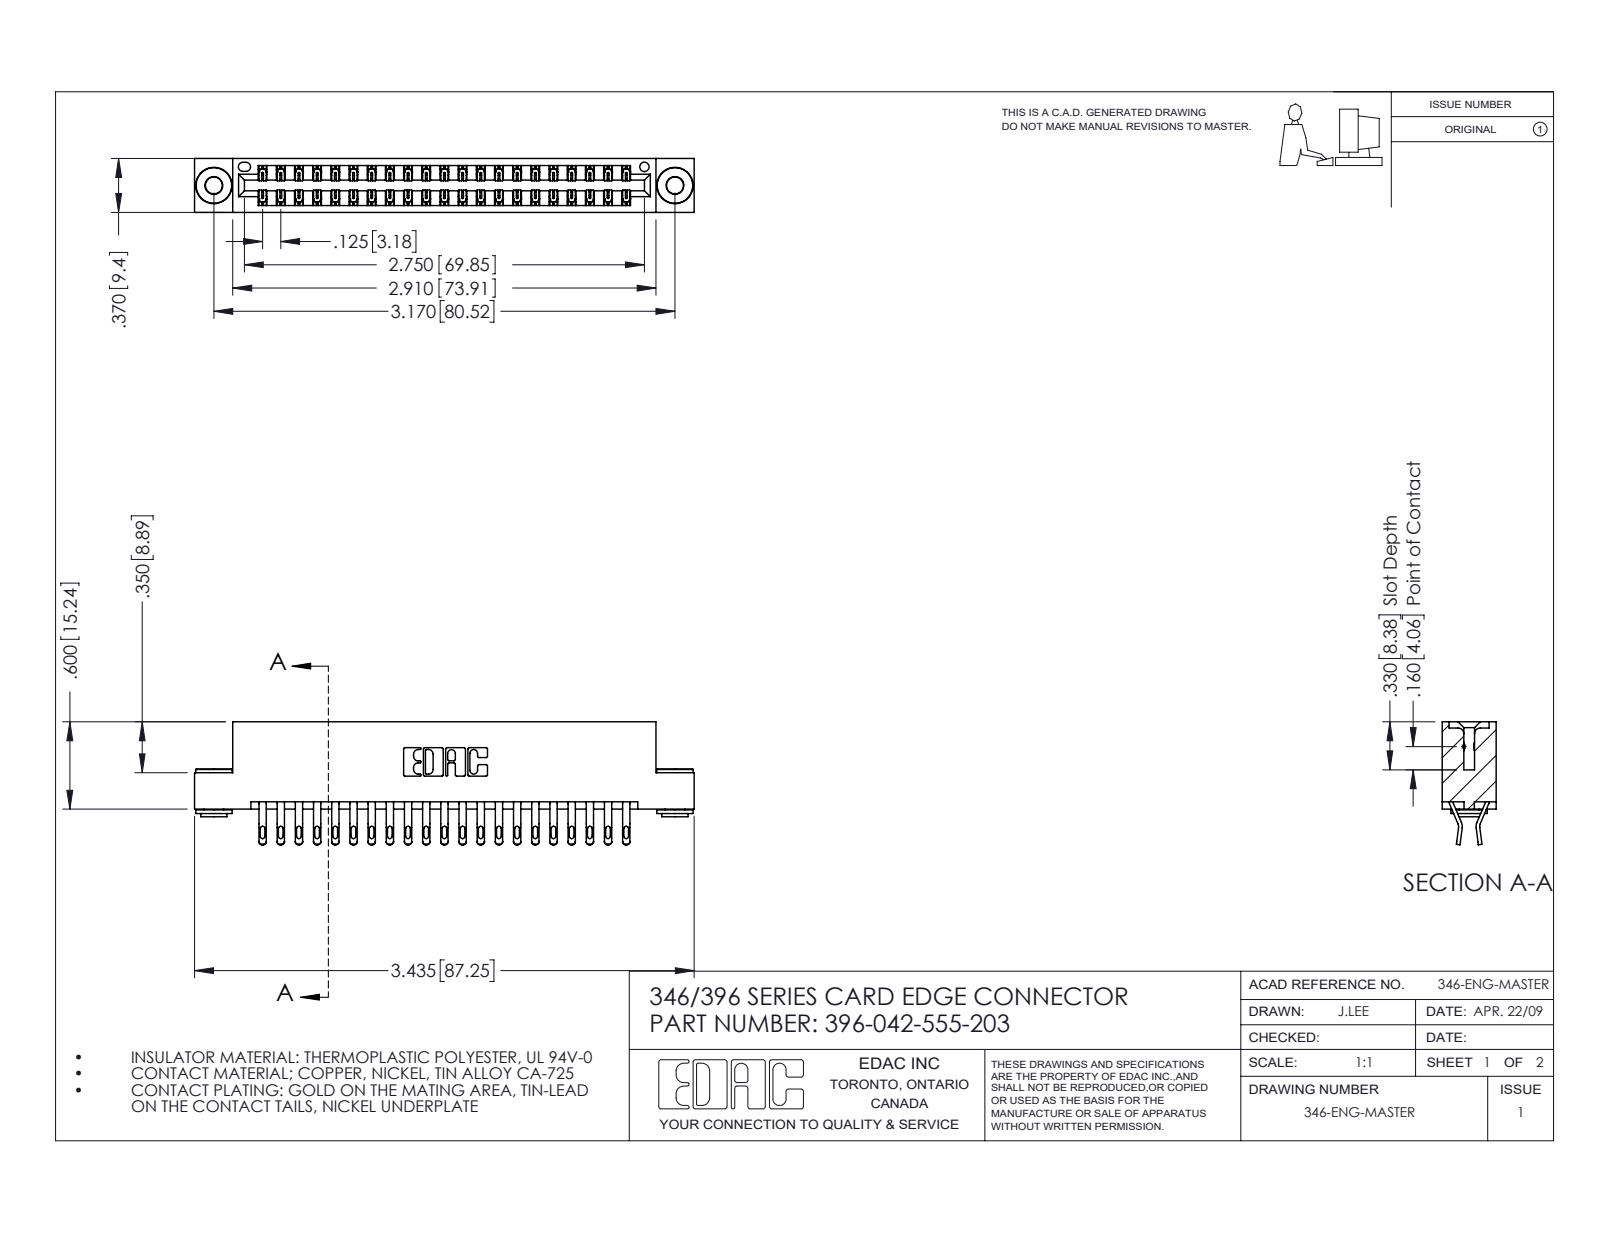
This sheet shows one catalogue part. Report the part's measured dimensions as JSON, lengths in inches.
{"part_name": "345-292-001_555 Tail; 346 Part_Flush Mounting Lugs - 0.156 Dia-TH; 396-042-555-203; 345-250-002_345-250-002-102", "step_written_by": "SolidWorks 2016 (CONFIG_CONTROL_DESIGN)", "units": "inches", "bodies": {"solids": 45, "faces": 2596, "planar": 1472, "cylindrical": 1116, "other": 8}, "overall_size": [3.435, 0.845, 0.37], "volume_in3": 0.518, "surface_area_in2": 18.57, "round_holes": [[0.116, 2], [0.156, 2], [0.064, 1]], "round_bosses_or_shafts": [[0.25, 2], [0.18, 2], [0.136, 2]], "partial_cylinders_radius": [[0.016, 84], [0.02, 84], [0.006, 63], [0.01, 22], [0.007, 6], [0.031, 6], [0.026, 3], [0.01, 2]], "face_to_face_distances": [0.048, 0.322, 0.25, 0.37, 0.025, 0.072, 0.298, 0.275, 0.148, 0.222], "hole_center_spacings": [0.246, 2.963, 3.17]}
